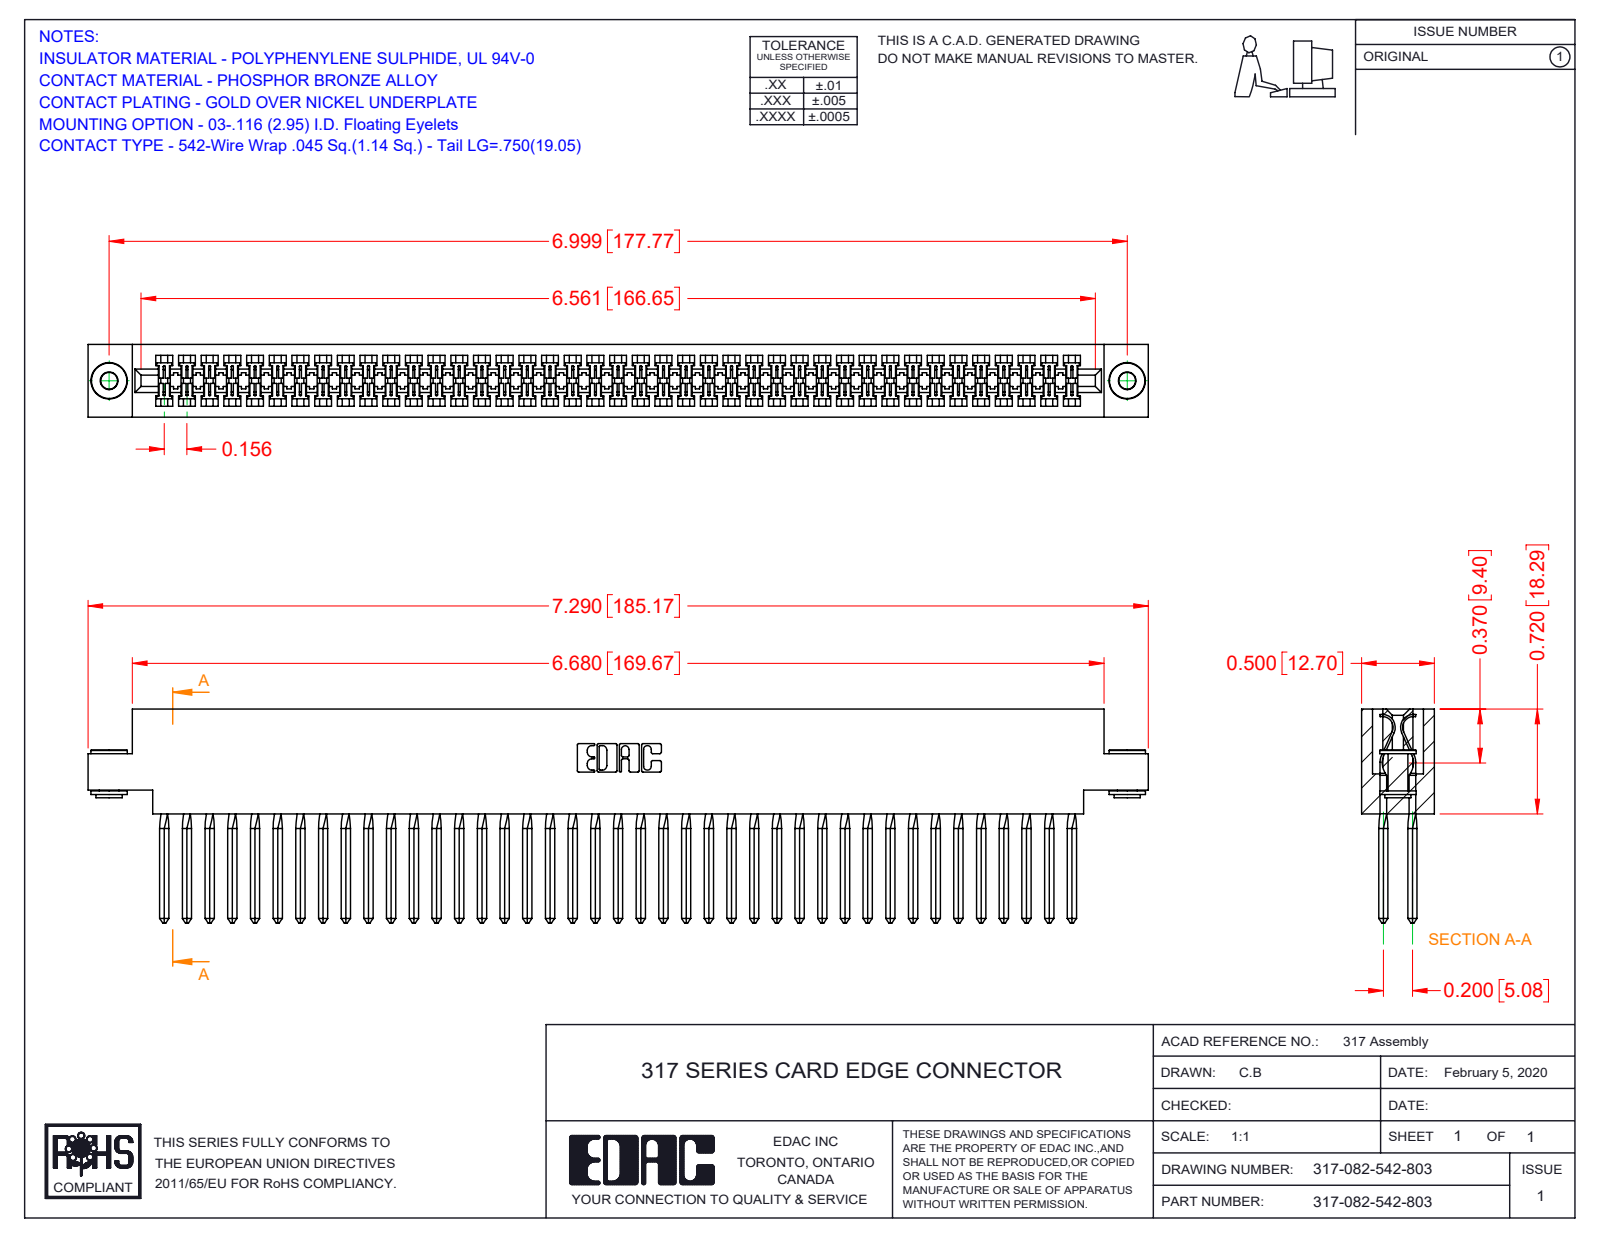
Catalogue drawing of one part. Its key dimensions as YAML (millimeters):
part_name: "345-250-002_345-250-002-102; 317 Part_.156 Dia - TH; 317-290-003_542; 317-082-542-803"
step_written_by: "SolidWorks 2016 (CONFIG_CONTROL_DESIGN)"
units: millimeters
bodies: {solids: 85, faces: 4814, planar: 3840, cylindrical: 638, other: 336}
overall_size: [185.2, 37.3, 12.7]
volume: 30320
surface_area: 42330
round_holes:
  - {diameter: 2.9, count: 2}
  - {diameter: 4, count: 2}
round_bosses_or_shafts:
  - {diameter: 6.4, count: 2}
  - {diameter: 4.6, count: 2}
  - {diameter: 3.5, count: 2}
partial_cylinders:
  - {radius: 0.2, count: 164}
  - {radius: 0.3, count: 22}
  - {radius: 0.2, count: 6}
  - {radius: 0.8, count: 6}
  - {radius: 0.7, count: 3}
  - {radius: 1.9, count: 2}
  - {radius: 2.3, count: 2}
  - {radius: 2.5, count: 2}
face_to_face_distances: [12.7, 1.9, 10.8, 8.9, 5.1, 1.2, 3.3, 9.4, 1.3, 7.5]
hole_center_spacings: [177.8]
